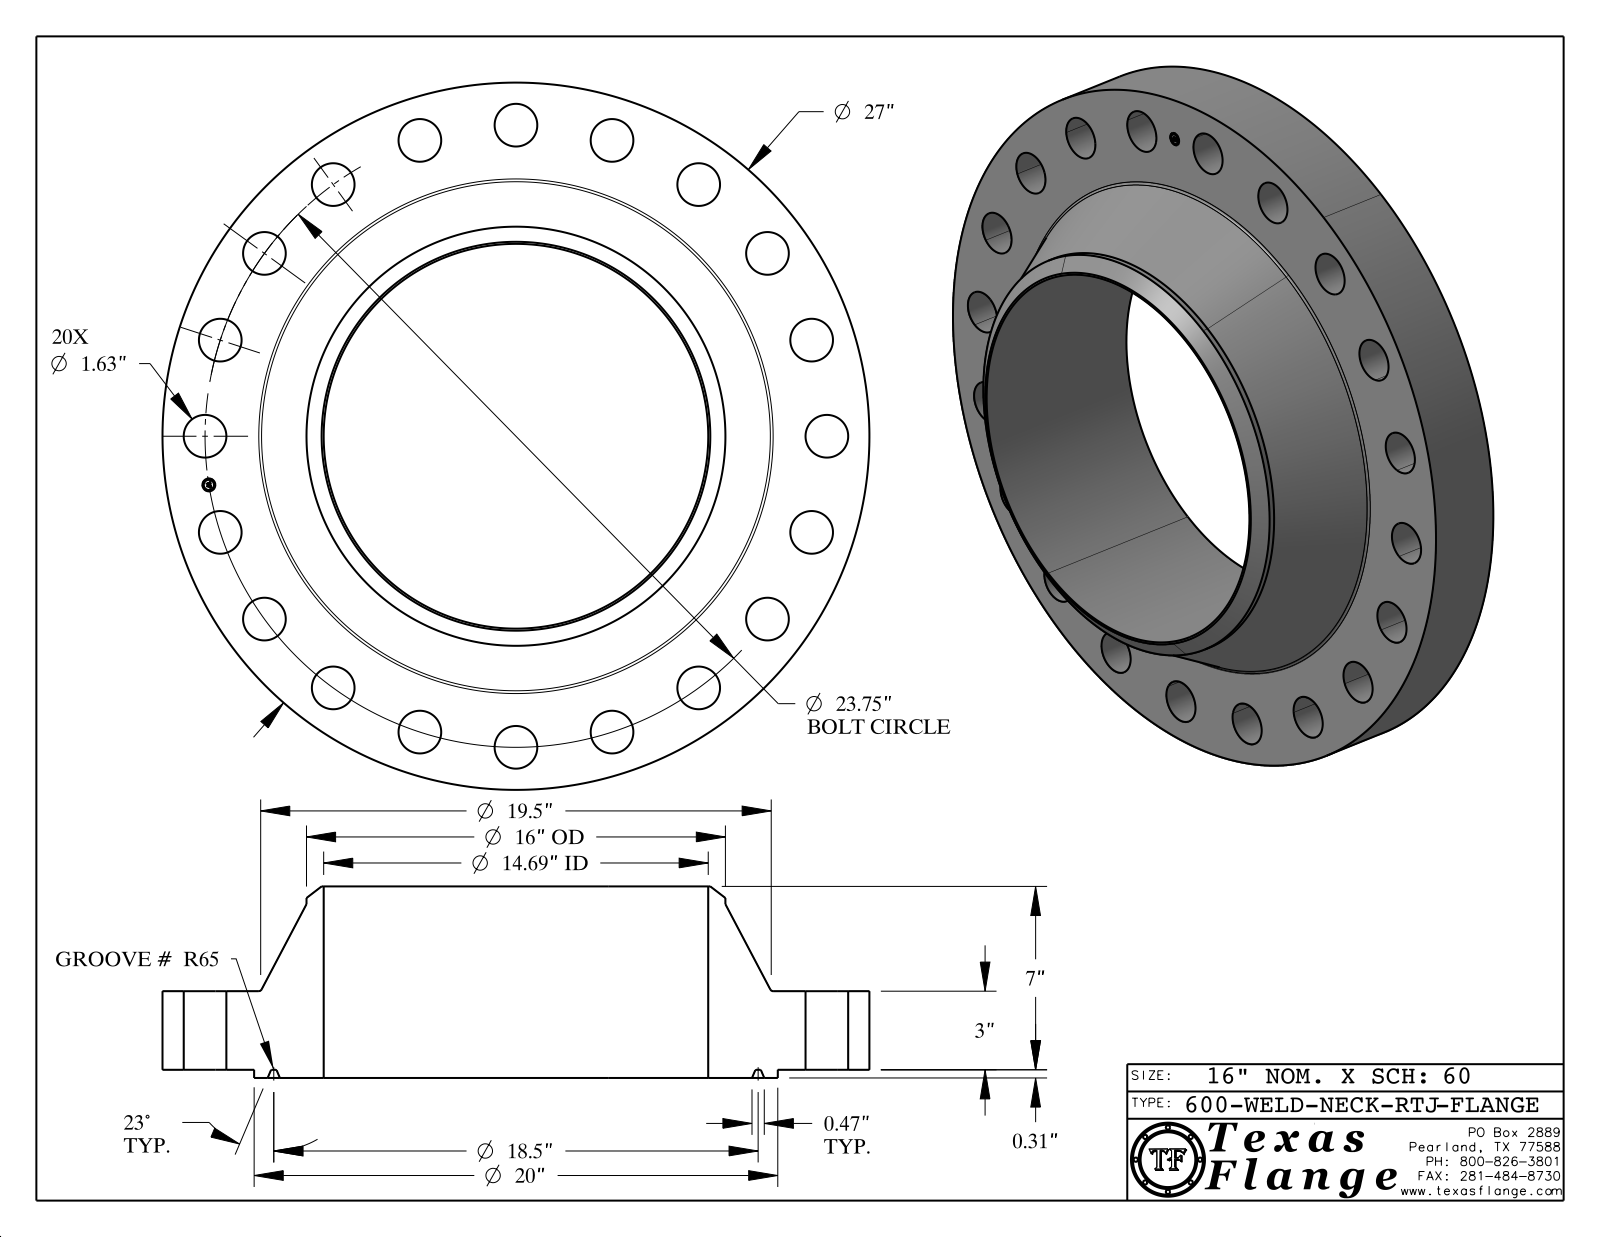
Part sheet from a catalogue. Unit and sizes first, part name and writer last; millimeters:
Units: millimetres
Overall size (bounding box): 685.8 × 685.8 × 185.8
Round holes (diameter × count): ⌀41.4 ×20, ⌀12.6 ×1, ⌀373.1 ×1
Round bosses / shafts (diameter × count): ⌀0.8 ×8, ⌀685.8 ×1, ⌀508 ×1, ⌀406.4 ×1, ⌀9.9 ×1
Main face-to-face distances: 76.2, 8, 84.2, 185.8, 177.8, 101.6, 83.8, 75.8, 0.4, 102
Hole centre spacings: 301.6, 426.6, 488, 573.7, 595.8, 186.4, 273.9, 94.4
Volume: 22 940 000 mm³ · Surface area: 1 158 000 mm²
Bodies: 1 solid, 453 faces (371 planar, 68 cylindrical, 14 other)
Part name (STEP PRODUCT): 600-WELD-NECK-RTJ
STEP written by: CATIA V5 STEP AP214 (AUTOMOTIVE_DESIGN)
